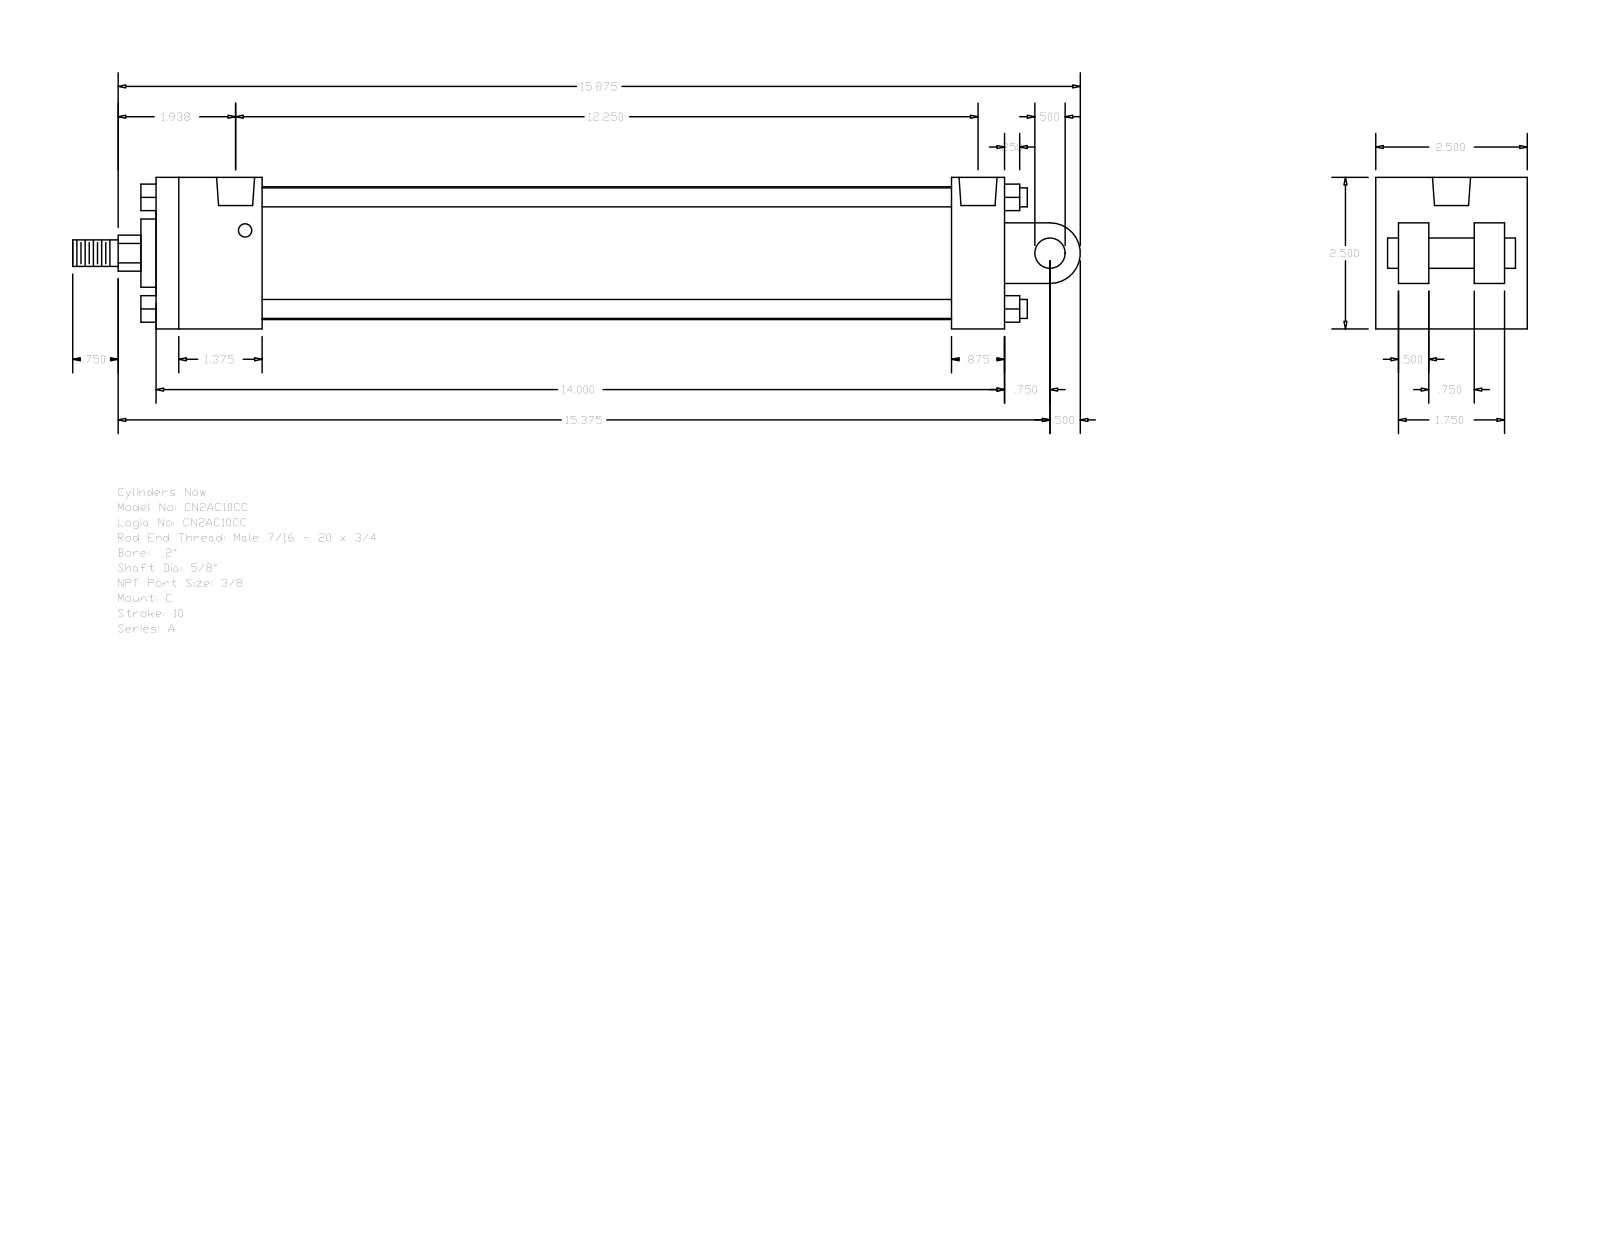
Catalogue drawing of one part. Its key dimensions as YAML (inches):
part_name: "A_C__0200_0.625"
step_written_by: "GSSL Pune (CONFIG_CONTROL_DESIGN)"
units: inches
bodies: {solids: 0, faces: 135, planar: 102, cylindrical: 33, other: 0}
overall_size: [16.625, 2.5, 2.5]
round_holes:
  - {diameter: 0.219, count: 4}
  - {diameter: 0.627, count: 2}
round_bosses_or_shafts:
  - {diameter: 0.313, count: 4}
  - {diameter: 2.19, count: 1}
  - {diameter: 1.125, count: 1}
  - {diameter: 0.625, count: 1}
  - {diameter: 0.5, count: 1}
  - {diameter: 0.437, count: 1}
partial_cylinders:
  - {radius: 0.297, count: 1}
  - {radius: 0.5, count: 1}
face_to_face_distances: [2.5, 14, 1.75, 0.375, 12.25, 13.125, 11.375, 0.875, 0.5, 2.125]
hole_center_spacings: [11.937, 0.156, 0.157, 12.093, 12.094, 12.25]
